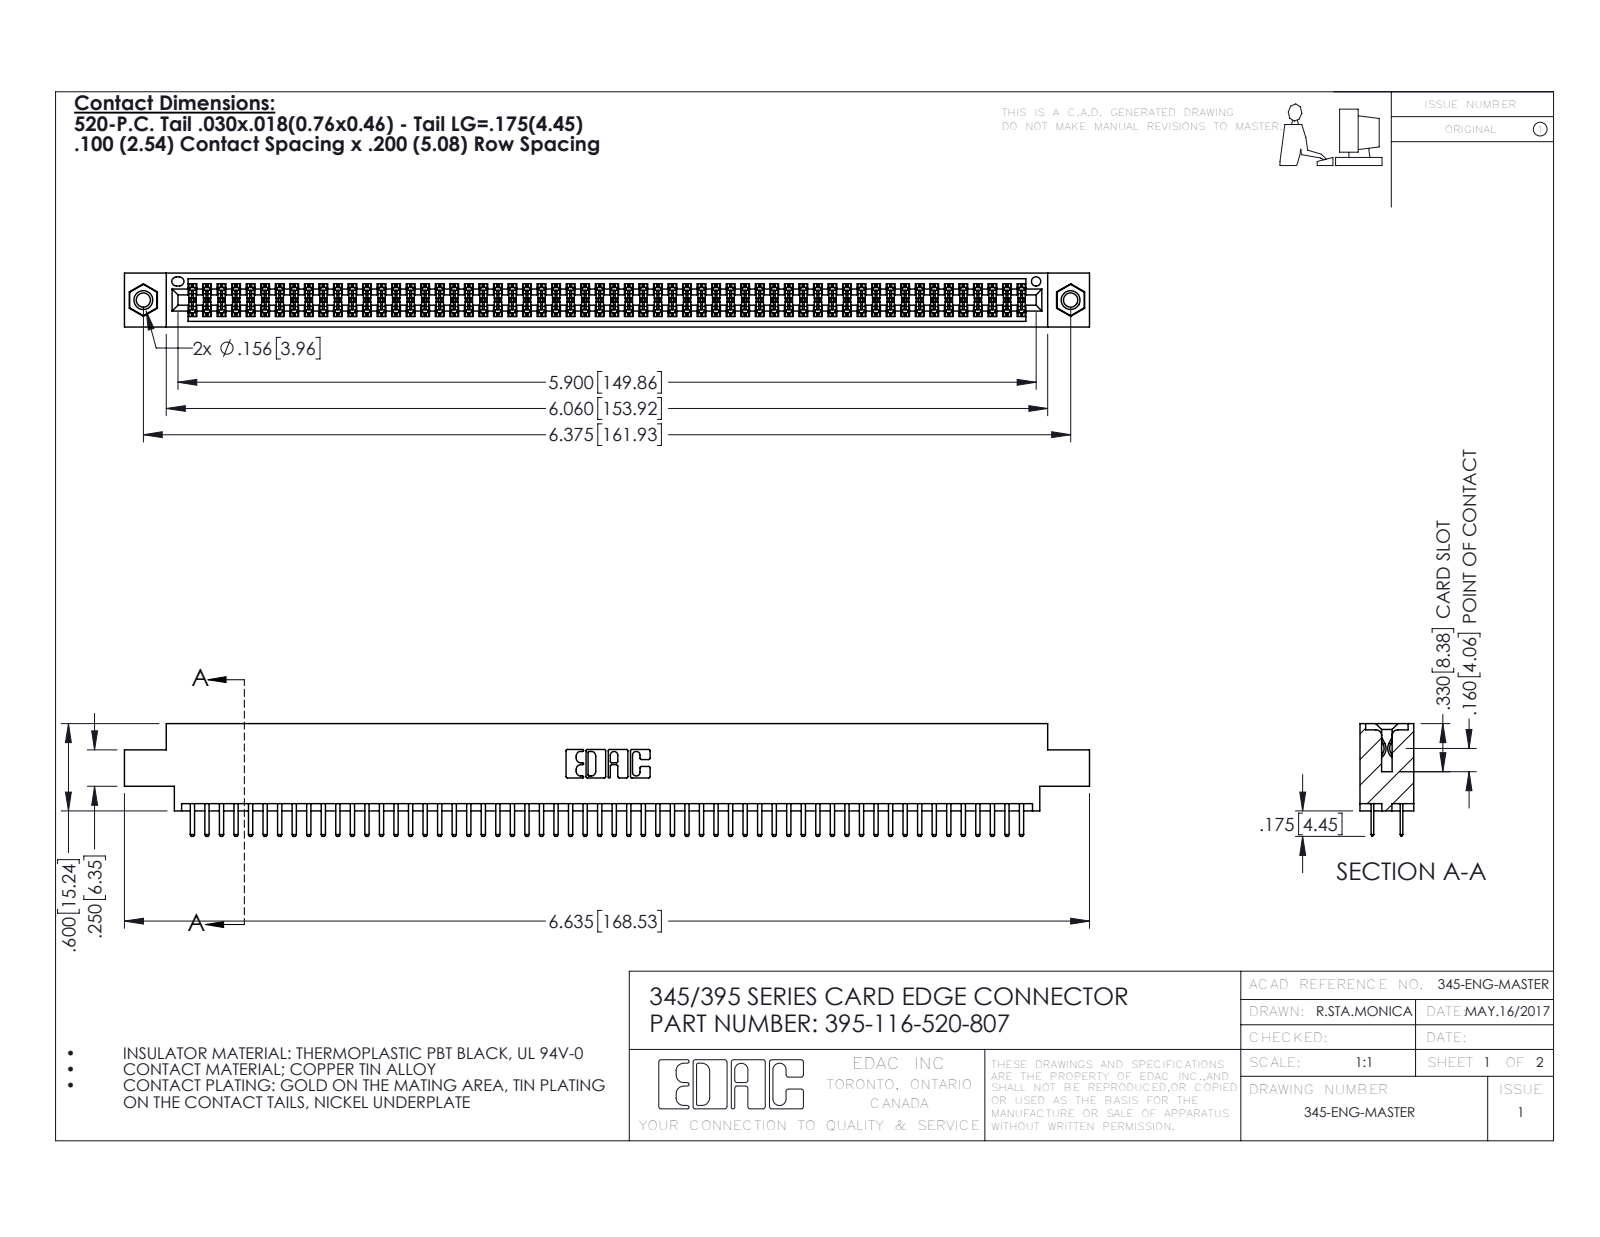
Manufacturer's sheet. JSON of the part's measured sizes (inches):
{"part_name": "345-292-001_345-293-120; 345-250-001_345-250-005-103; 345 Part_0.170 Offset - 0.156 Dia-TI; 395-116-520-807", "step_written_by": "SolidWorks 2016 (CONFIG_CONTROL_DESIGN)", "units": "inches", "bodies": {"solids": 119, "faces": 6454, "planar": 4176, "cylindrical": 2262, "other": 16}, "overall_size": [6.635, 0.775, 0.37], "volume_in3": 0.997, "surface_area_in2": 38.02, "round_holes": [[0.098, 2], [0.125, 2], [0.156, 2], [0.064, 1]], "round_bosses_or_shafts": [[0.155, 2]], "partial_cylinders_radius": [[0.006, 174], [0.01, 120], [0.01, 22], [0.007, 6], [0.031, 6], [0.026, 3], [0.014, 2], [0.019, 2]], "face_to_face_distances": [0.072, 0.298, 0.2, 0.37, 0.098, 0.272, 0.025, 0.225, 0.022, 0.072], "hole_center_spacings": [0.27, 6.139, 6.375]}
